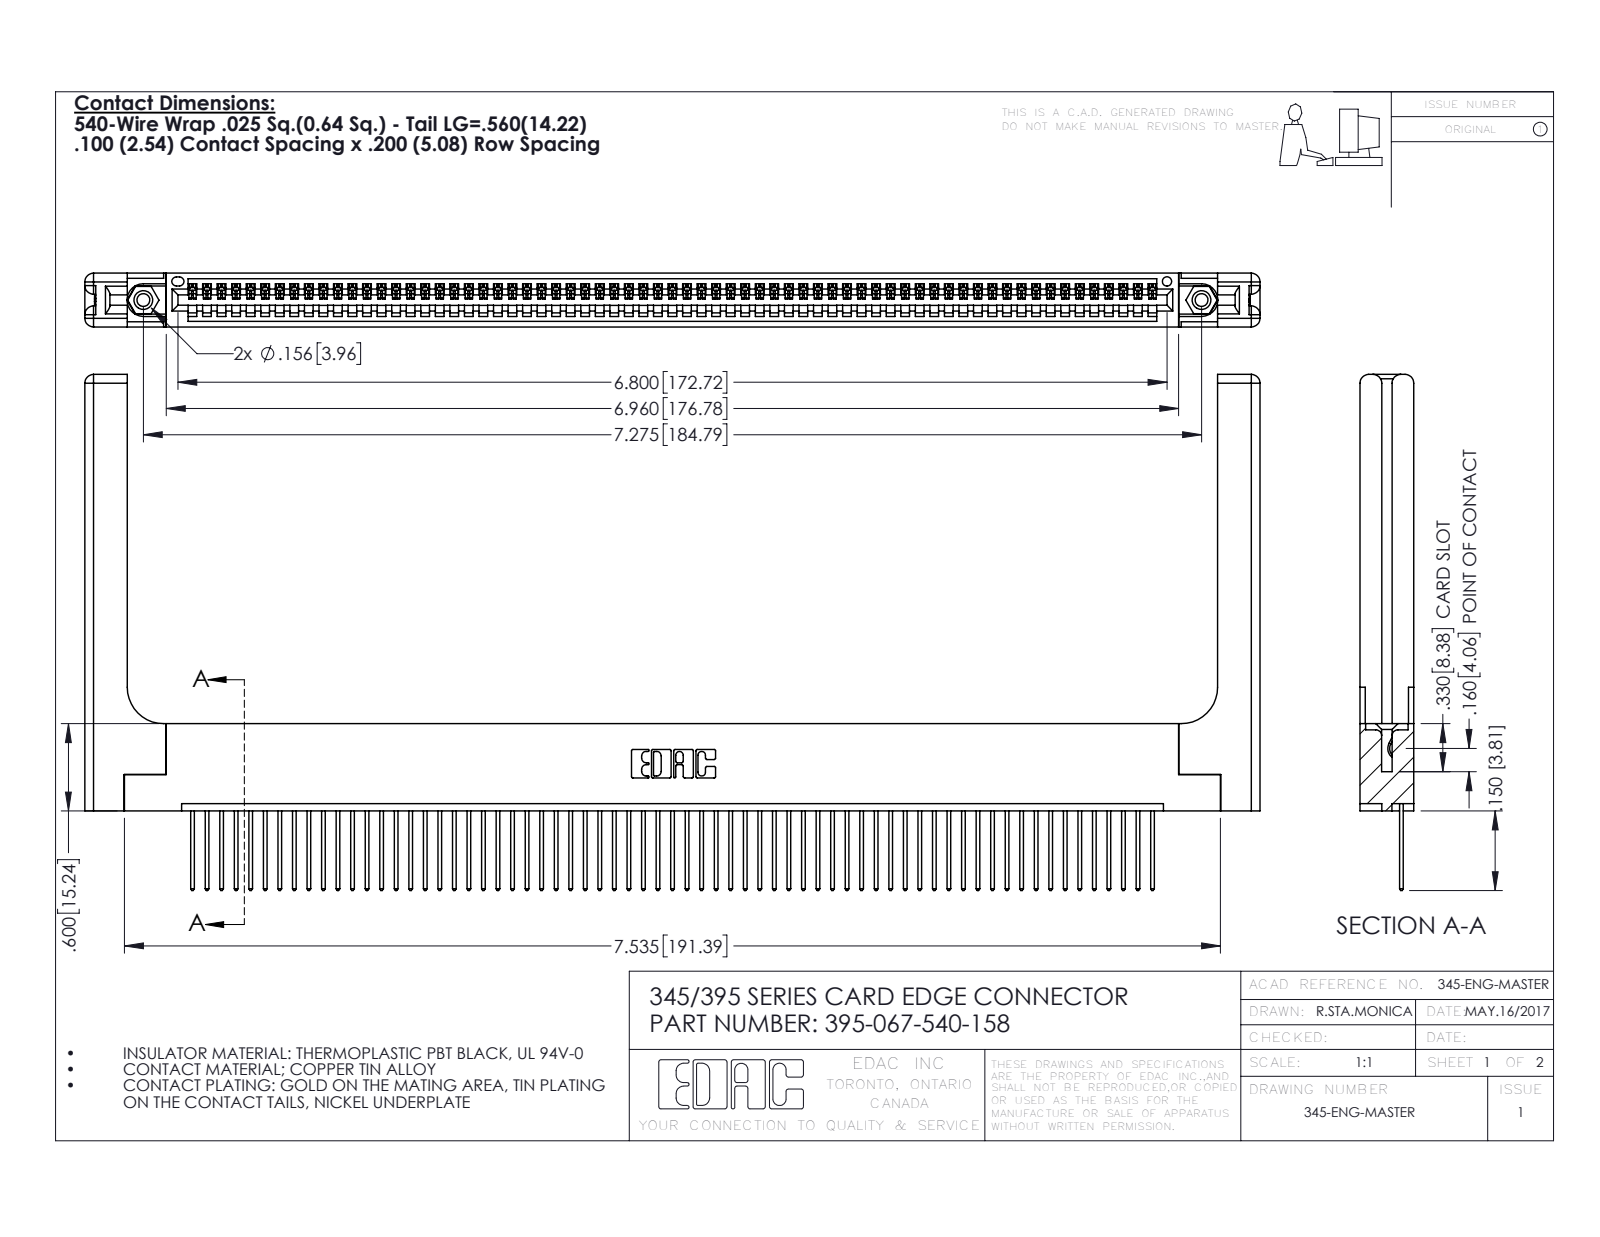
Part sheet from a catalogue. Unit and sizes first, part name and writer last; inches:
Units: inches
Overall size (bounding box): 8.079 × 3.547 × 0.37
Round holes (diameter × count): ⌀0.089 ×2, ⌀0.125 ×2, ⌀0.156 ×2, ⌀0.064 ×1
Round bosses / shafts (diameter × count): ⌀0.155 ×2
Partial cylindrical surfaces — rounded edges, fillets, slot ends (radius × count): R0.006 ×134, R0.01 ×134, R0.01 ×22, R0.06 ×16, R0.007 ×6, R0.031 ×6, R0.026 ×3, R0.03 ×2
Main face-to-face distances: 0.072, 0.298, 0.37, 0.098, 0.272, 0.025, 0.2, 0.225, 0.148, 0.15
Hole centre spacings: 0.27, 7.039, 7.275
Volume: 1.726 in³ · Surface area: 50.52 in²
Bodies: 72 solids, 4268 faces (2908 planar, 1300 cylindrical, 60 other)
Part name (STEP PRODUCT): 345-292-001_345-293-140; 345-220-058_345-220-058; 345-250-001_345-250-001-102; 395-067-540-158 (+1 more)
STEP written by: SolidWorks 2016 (CONFIG_CONTROL_DESIGN)
